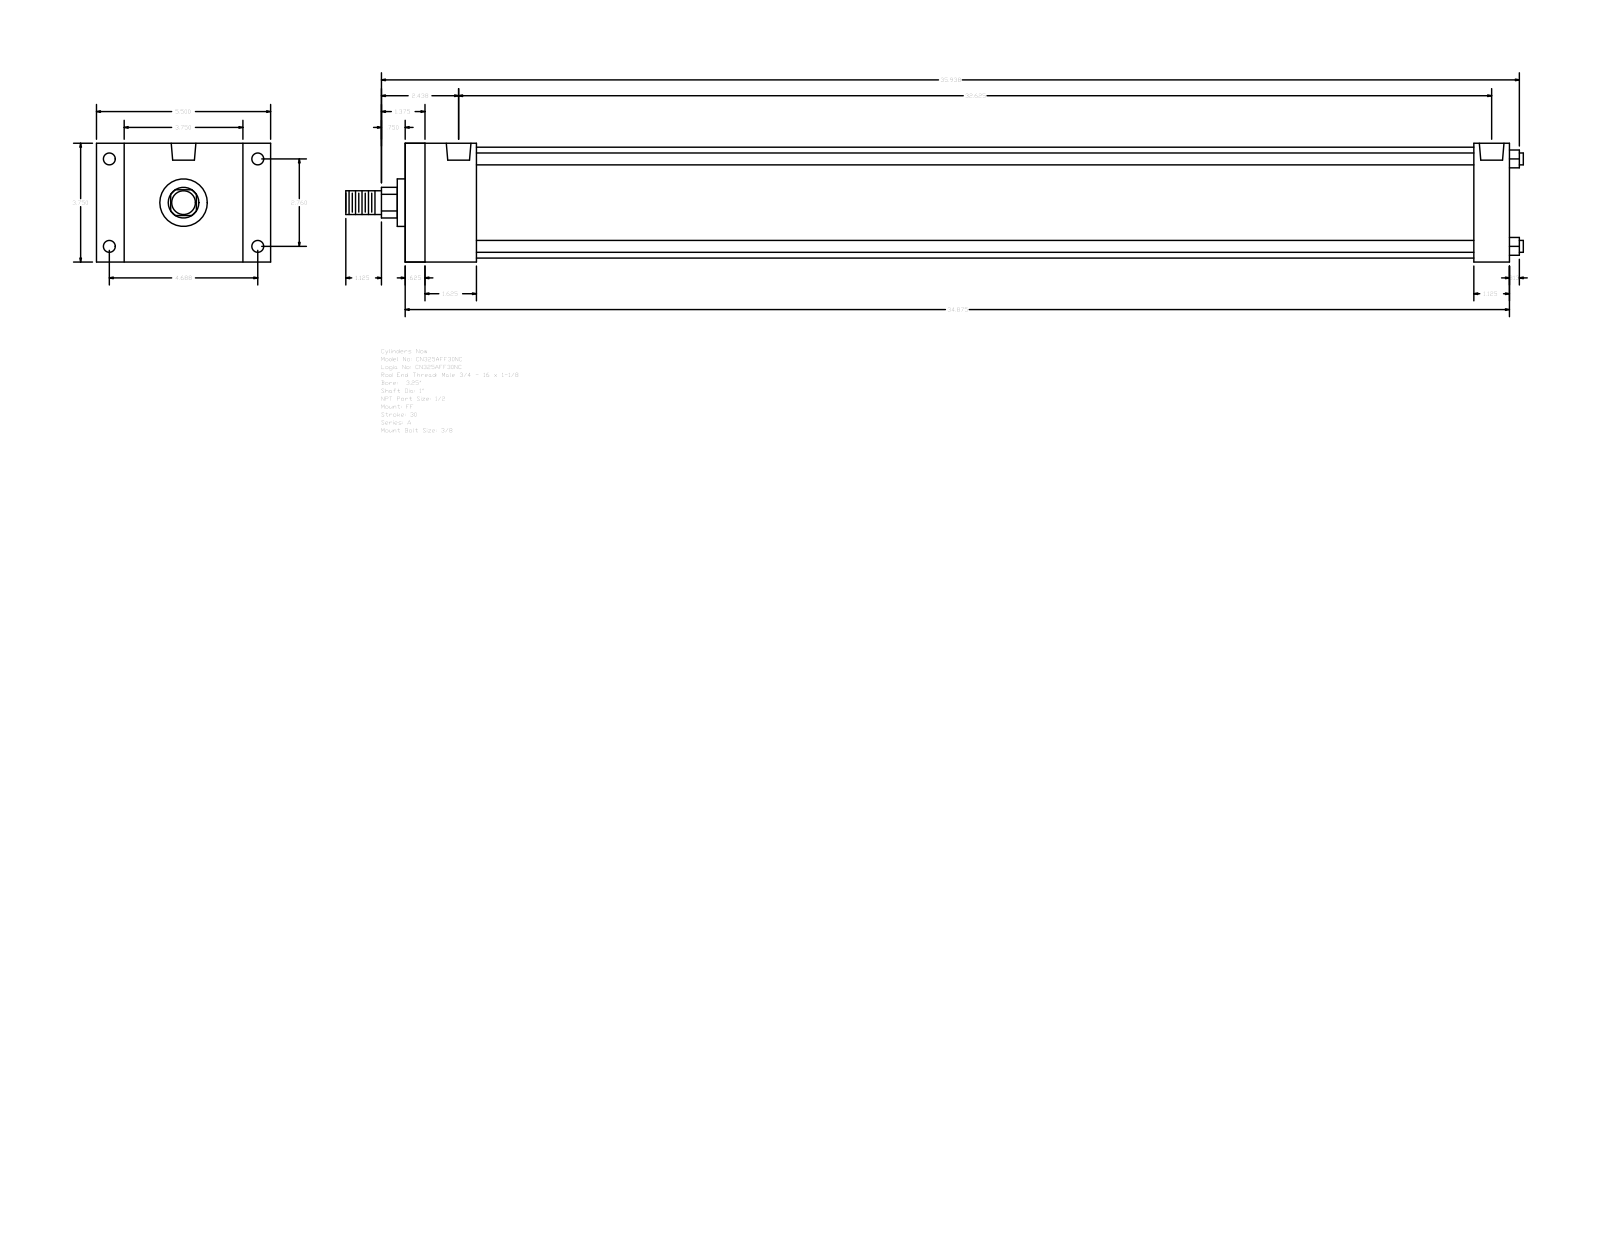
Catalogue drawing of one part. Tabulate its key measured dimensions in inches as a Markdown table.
| quantity | value |
| --- | --- |
| part name | A_FF__0325_1 |
| STEP written by | GSSL Pune (CONFIG_CONTROL_DESIGN) |
| units | inches |
| bodies | 0 solids, 92 faces (64 planar, 28 cylindrical, 0 other) |
| overall size | 37.187 × 5.5 × 3.75 |
| round holes (diameter × count) | 0.344 × 4, 0.375 × 4, 0.778 × 2 |
| round bosses / shafts (diameter × count) | 0.375 × 4, 3.5 × 1, 1.5 × 1, 1 × 1, 0.75 × 1 |
| partial cylindrical surfaces (radius × count) | 0.484 × 1 |
| main face-to-face distances | 3.75, 34.875, 0.625, 34.25, 0.875, 4.625, 2.25, 33.75, 1.625, 33.125 |
| hole center spacings | 0.125, 2.76, 4.687, 5.439, 32.375, 32.5, 32.625 |
